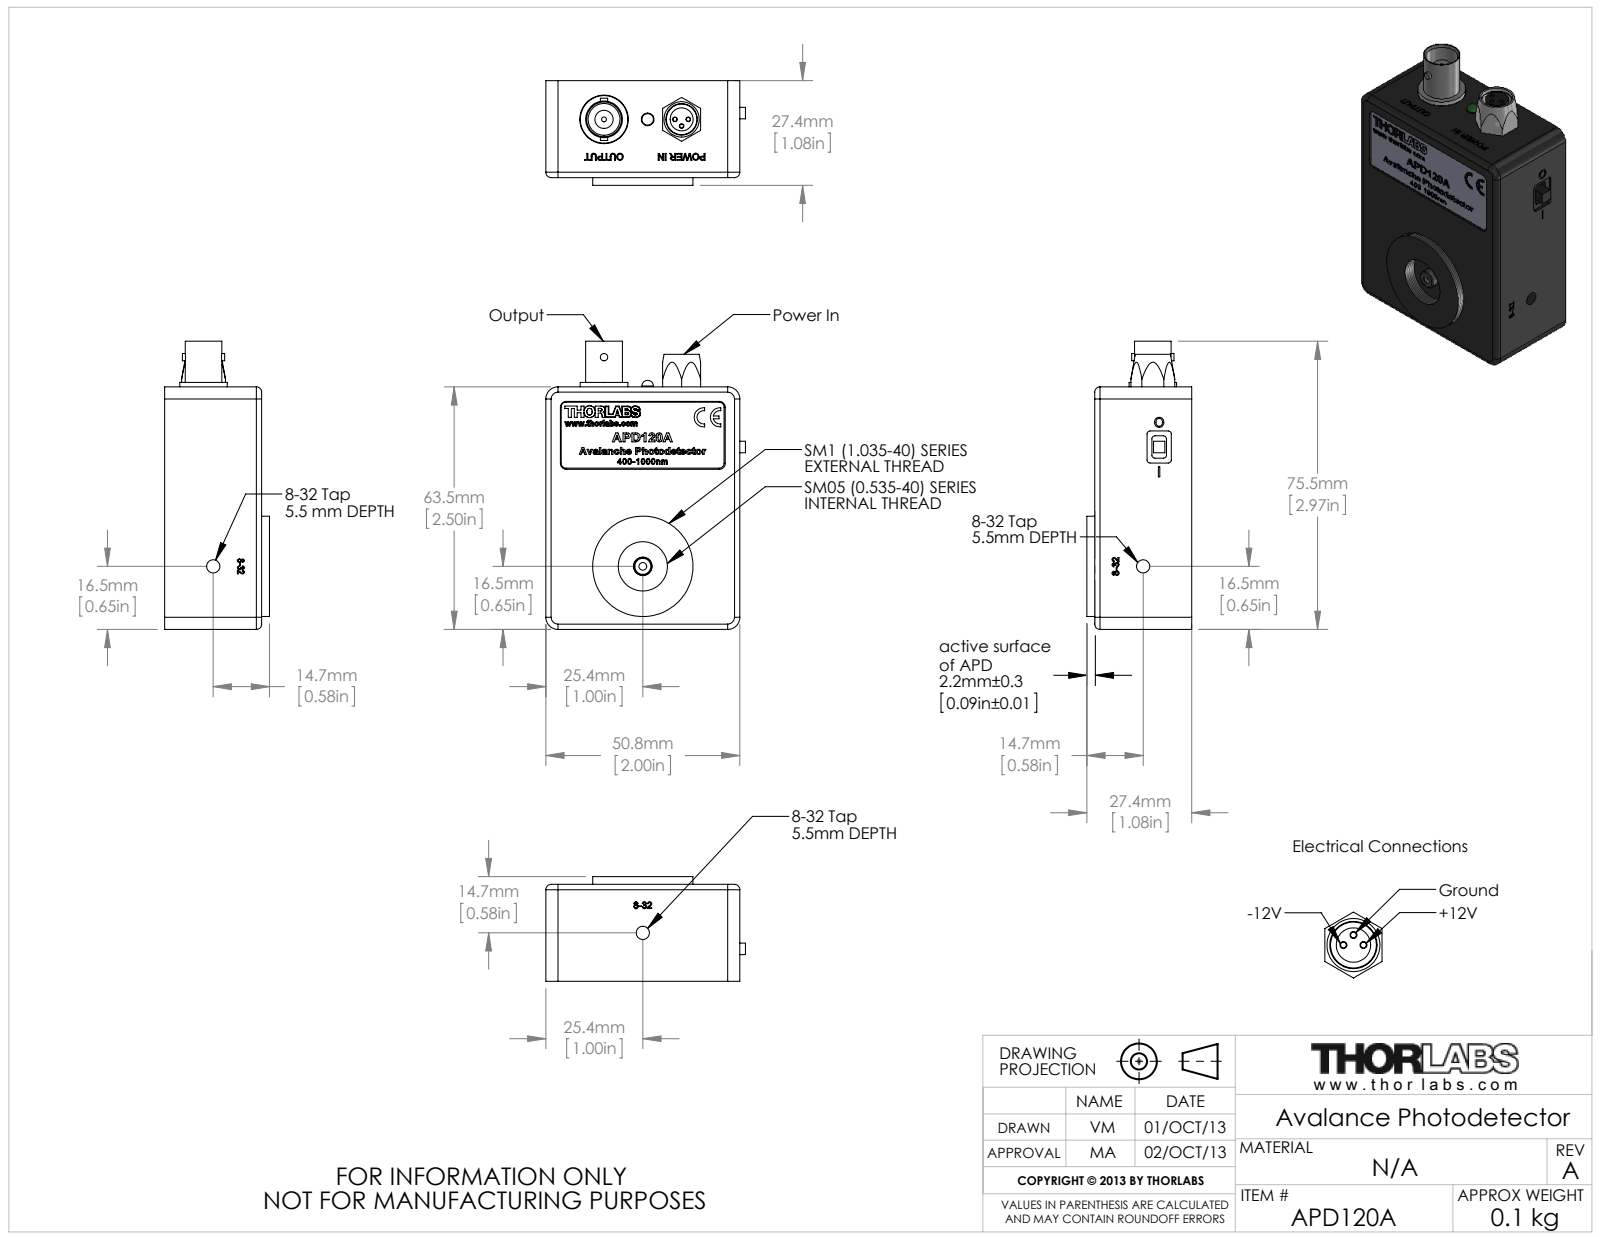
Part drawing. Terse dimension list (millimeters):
name: APD110A; APD120x-Folie_APD120A; countersunk flat head cross recess screw_din_ISO 7046-1 - M2 x 4 - Z --- 4N; M0092-0545-0A-Deckel (+7 more)
written by: SolidWorks 2012 (AUTOMOTIVE_DESIGN)
unit: mm
bodies: 74 solids, 2321 faces (1396 planar, 283 cylindrical, 642 other)
size: 75.46 × 52.26 × 27.43
volume: 39 530 mm³; area: 33 773 mm²
holes: 8× ⌀1.6, 4× ⌀2.4, 4× ⌀2.44, 3× ⌀0.46, 3× ⌀1, 3× ⌀1.02, 2× ⌀3.45, 1× ⌀1.27, 1× ⌀1.32, 1× ⌀2, 1× ⌀2.5, 1× ⌀3.3
bosses: 6× ⌀0.51, 5× ⌀3.8, 4× ⌀2, 3× ⌀0.45, 1× ⌀26.29, 1× ⌀12.45, 1× ⌀10.92, 1× ⌀9.6
rounds: 18× R3.17, 14× R3.3, 10× R0.8, 8× R0.79, 8× R1.91, 8× R2.41, 4× R1.27, 4× R1.4
face distances: 1.59, 11.49, 13.08, 2.54, 9.89, 1.6, 11.48, 25.4, 23.81, 13.92
hole spacings: 41.17, 39.38, 4.41, 20.89, 21.35, 51.14, 65.51, 1.27
